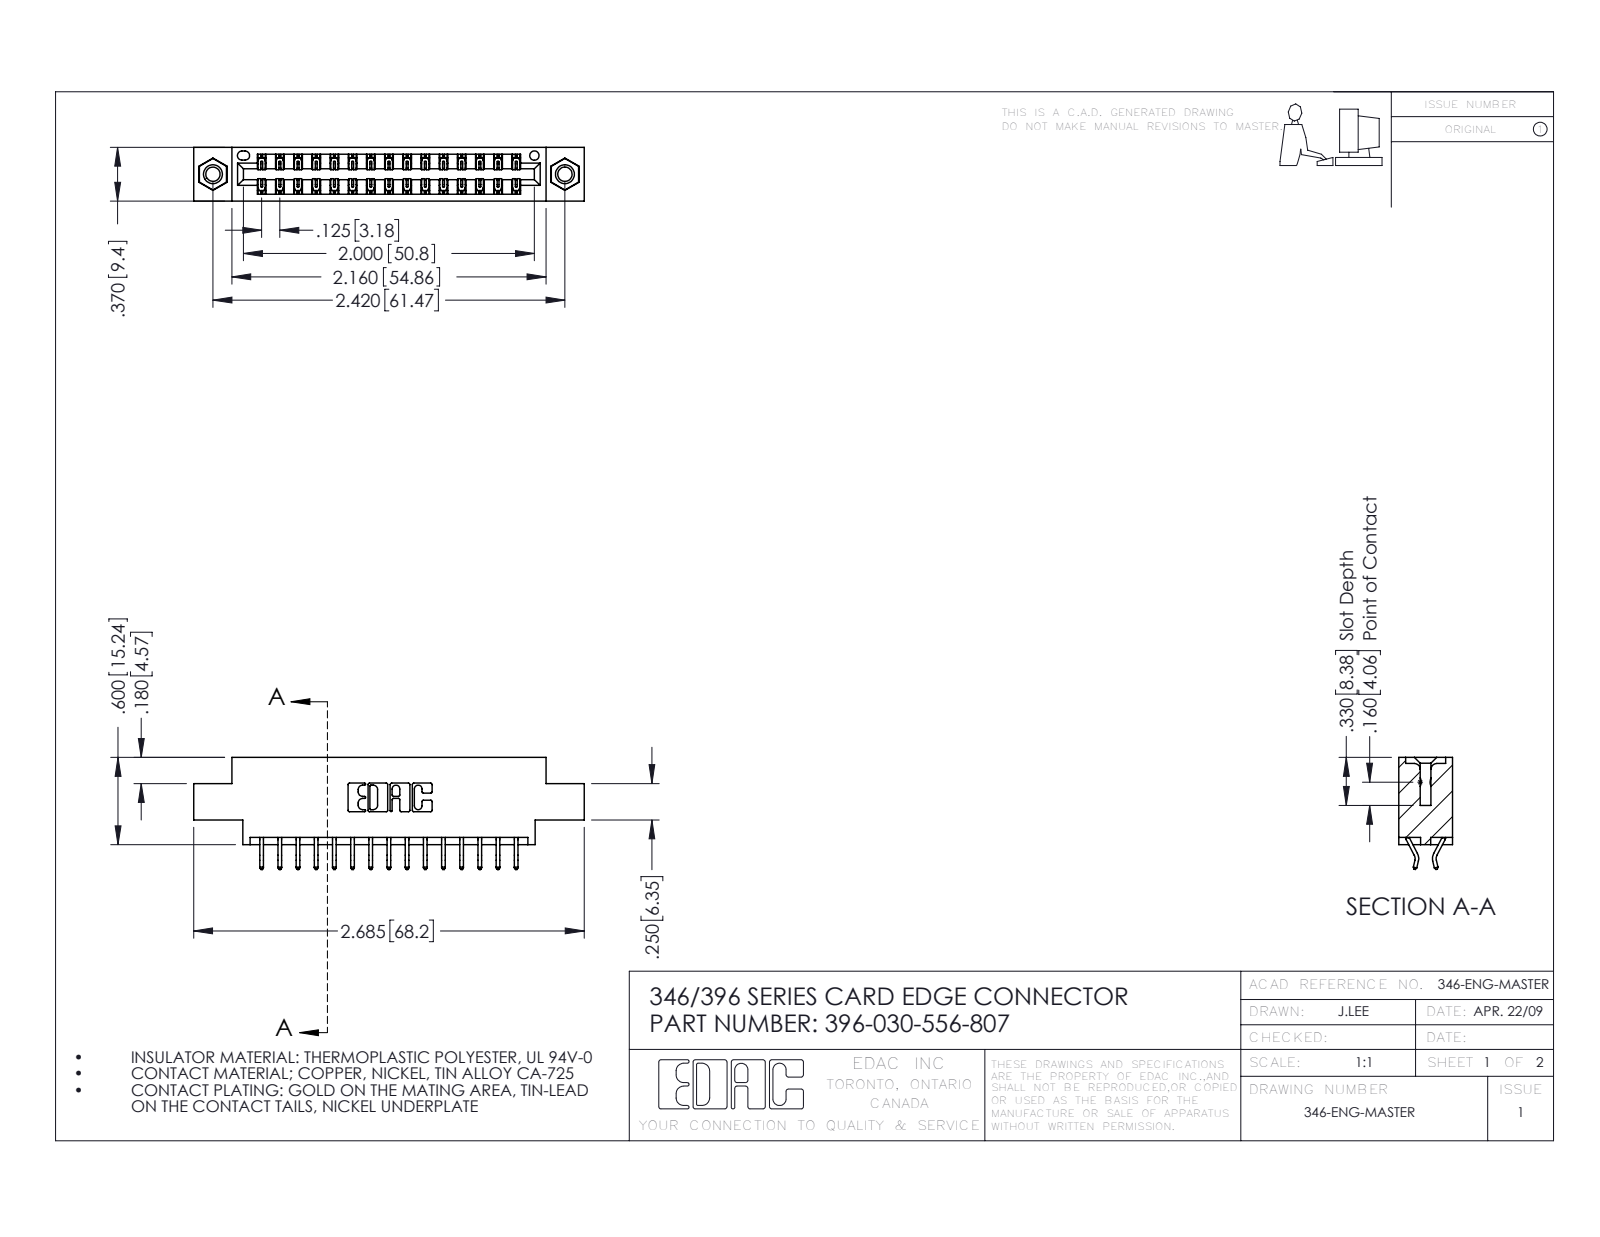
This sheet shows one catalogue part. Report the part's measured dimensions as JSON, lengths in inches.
{"part_name": "345-250-001_345-250-005-103; 345-292-001_556 Tail; 346 Part_0.170 Offset - 0.156 Dia-TI; 396-030-556-807", "step_written_by": "SolidWorks 2016 (CONFIG_CONTROL_DESIGN)", "units": "inches", "bodies": {"solids": 33, "faces": 1926, "planar": 1282, "cylindrical": 628, "other": 16}, "overall_size": [2.685, 0.77, 0.37], "volume_in3": 0.383, "surface_area_in2": 12.99, "round_holes": [[0.098, 2], [0.125, 2], [0.156, 2], [0.064, 1]], "round_bosses_or_shafts": [[0.155, 2]], "partial_cylinders_radius": [[0.006, 45], [0.01, 22], [0.007, 6], [0.031, 6], [0.026, 3], [0.01, 2], [0.014, 2], [0.022, 2]], "face_to_face_distances": [0.048, 0.322, 0.37, 0.25, 0.025, 0.072, 0.298, 0.222, 0.275, 0.148], "hole_center_spacings": [0.246, 2.213, 2.42]}
